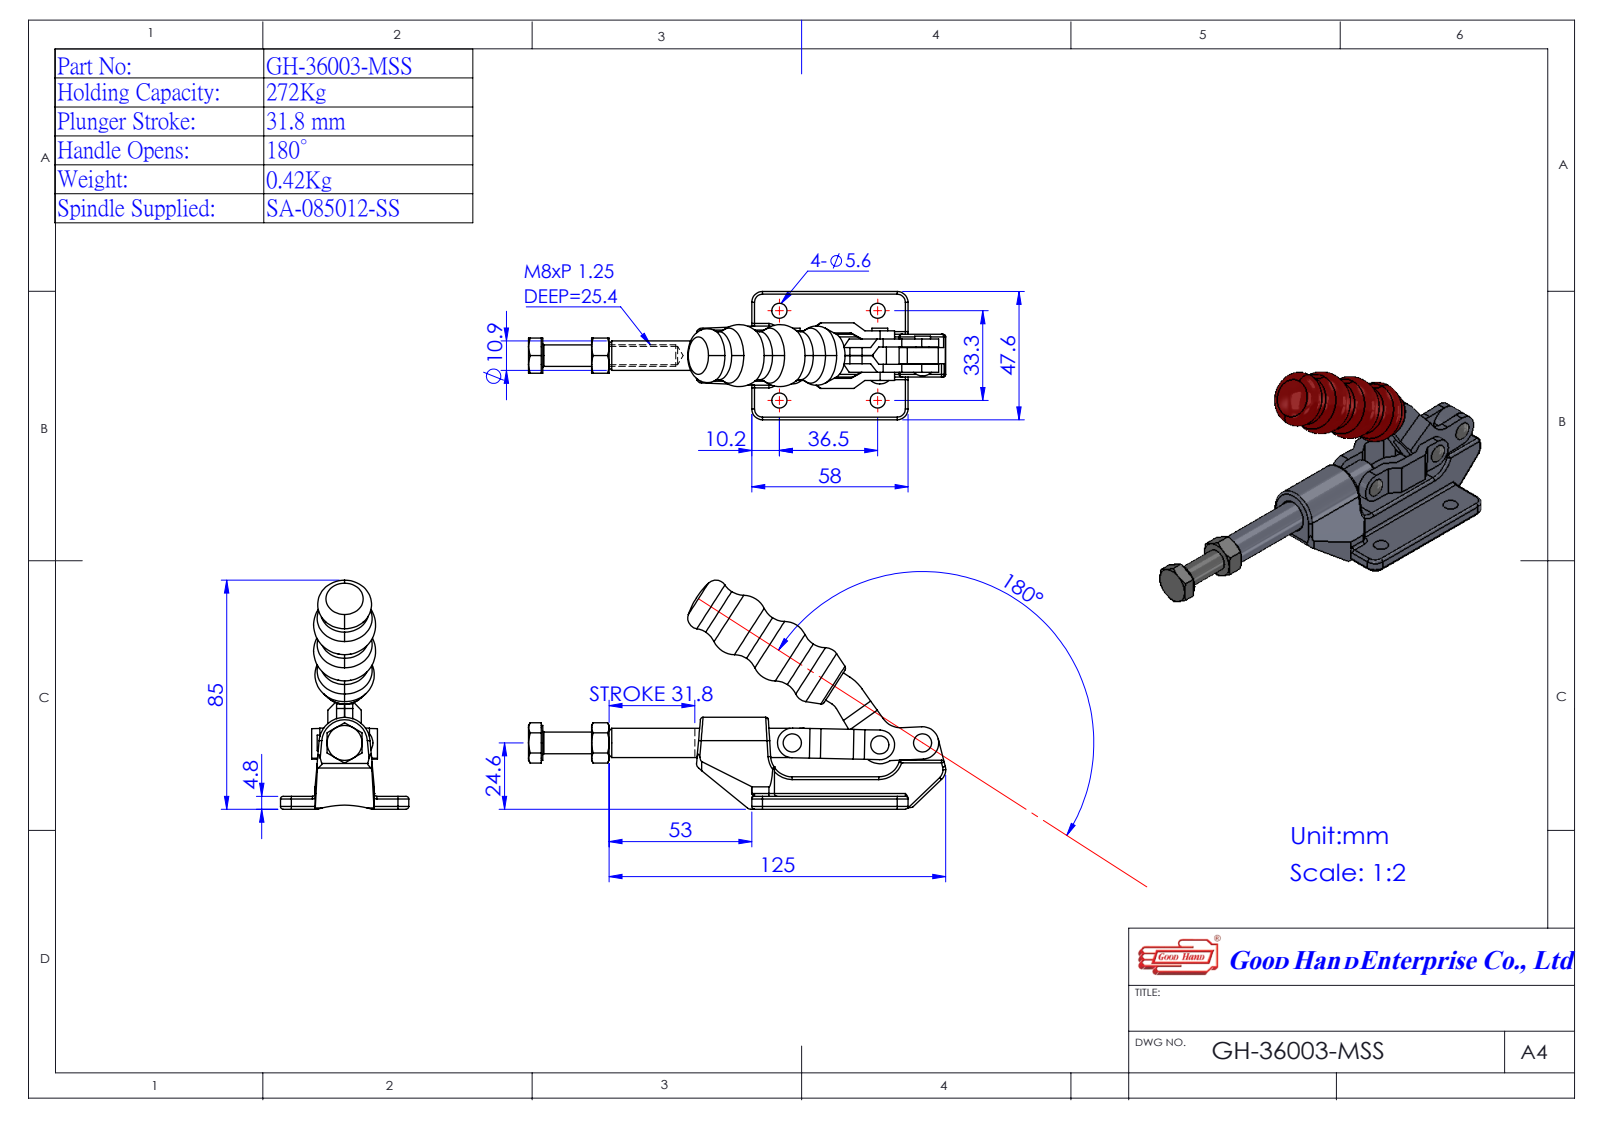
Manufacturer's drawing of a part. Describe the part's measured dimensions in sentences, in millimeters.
The part is named "Group3^EMC36003; Group2^EMC36003; EMC36003; Group4^EMC36003 (+1 more)". Its 3-D file was written by "SolidWorks 2016 (AUTOMOTIVE_DESIGN)". It is 4 solids with 308 faces: 114 planar, 95 cylindrical and 99 other. Overall it measures 152.4 by 82.39 by 47.6 millimeters. Its volume is 58 658 cubic millimeters and its surface area 31 419 square millimeters. Round holes: 4 of diameter 5.6, 3 of diameter 4.5, 1 of diameter 10. Round bosses or shafts: 3 of diameter 5.83, 1 of diameter 13, 1 of diameter 10.9, 1 of diameter 8. Partial cylindrical surfaces (rounded edges, fillets, slot ends): 8 of radius 1, 6 of radius 5, 3 of radius 8, 2 of radius 2, 2 of radius 4.52, 2 of radius 5.5, 2 of radius 6.02, 1 of radius 6. The main face-to-face distances are 3, 6.2, 3.2, 9.2, 6, 4.8, 2.68, 12.4, 9.4, 12.2. The hole center spacings are 33.3, 36.5, 49.41, 15.88, 32.51, 48.36.
